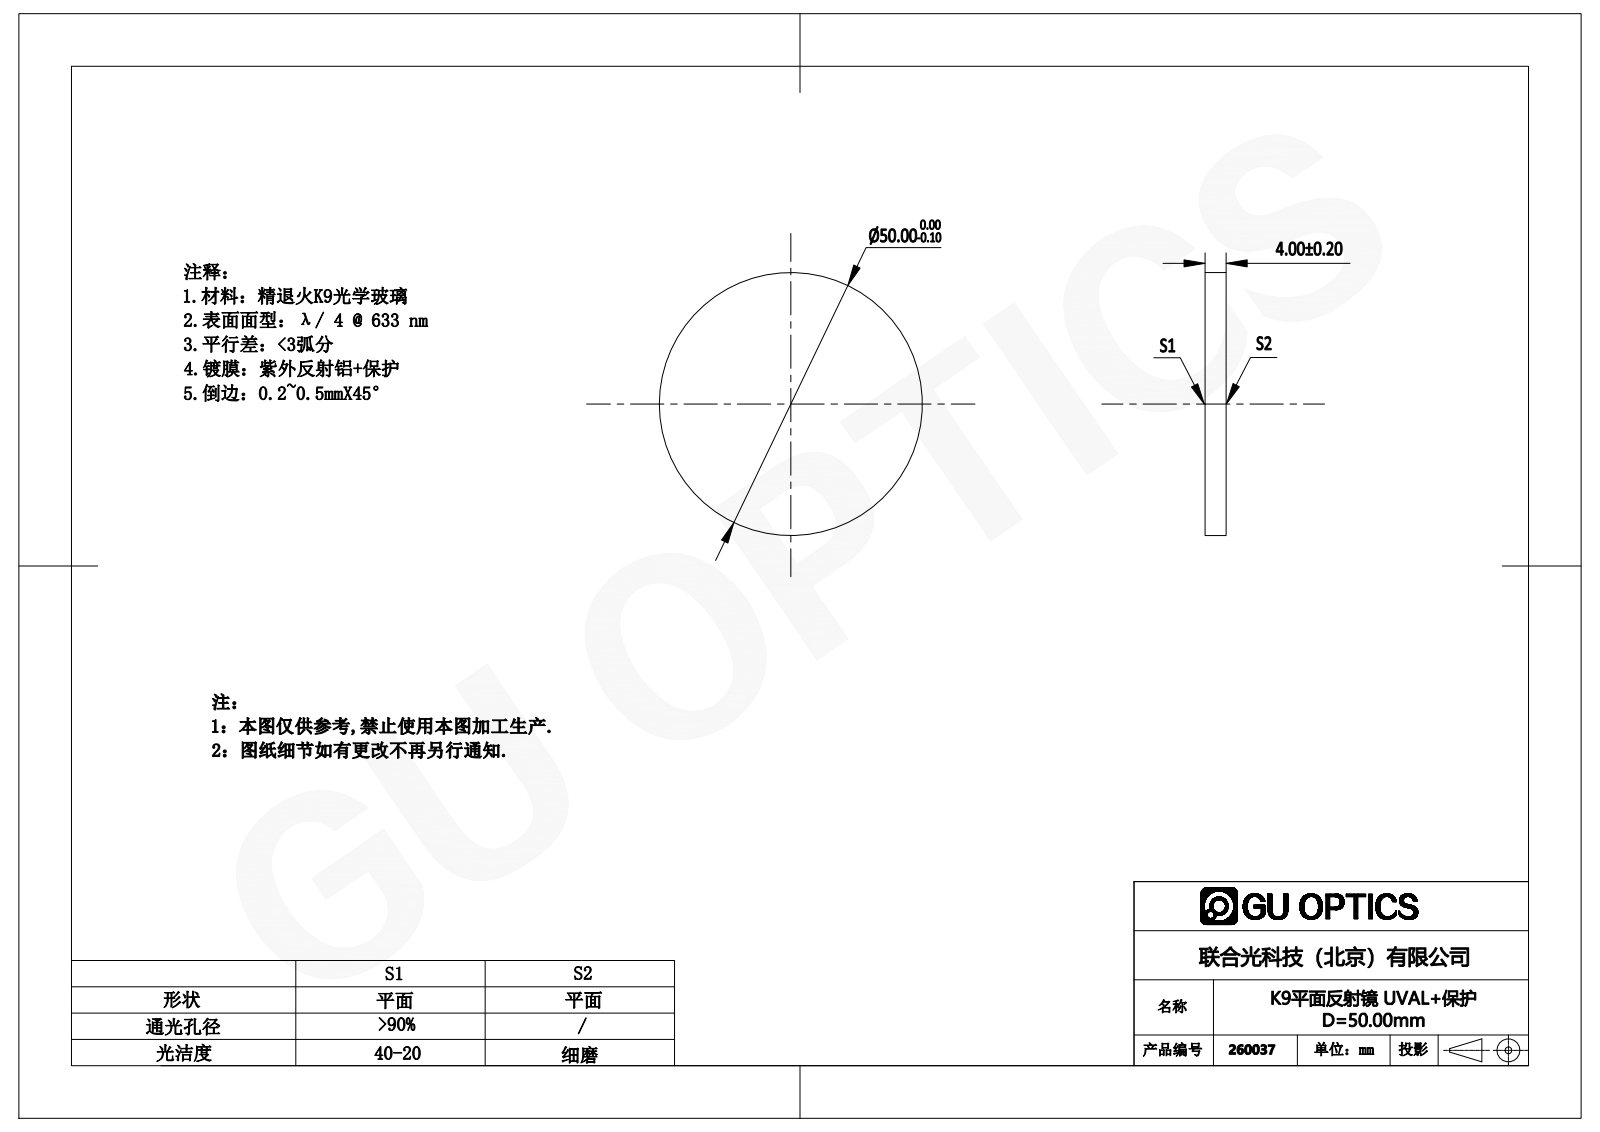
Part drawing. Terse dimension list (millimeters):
name: 260011
written by: SolidWorks 2016 (AUTOMOTIVE_DESIGN)
unit: mm
bodies: 1 solid, 4 faces (2 planar, 2 cylindrical, 0 other)
size: 50 × 50 × 4
volume: 7 854 mm³; area: 4 555 mm²
bosses: 1× ⌀50
face distances: 4
